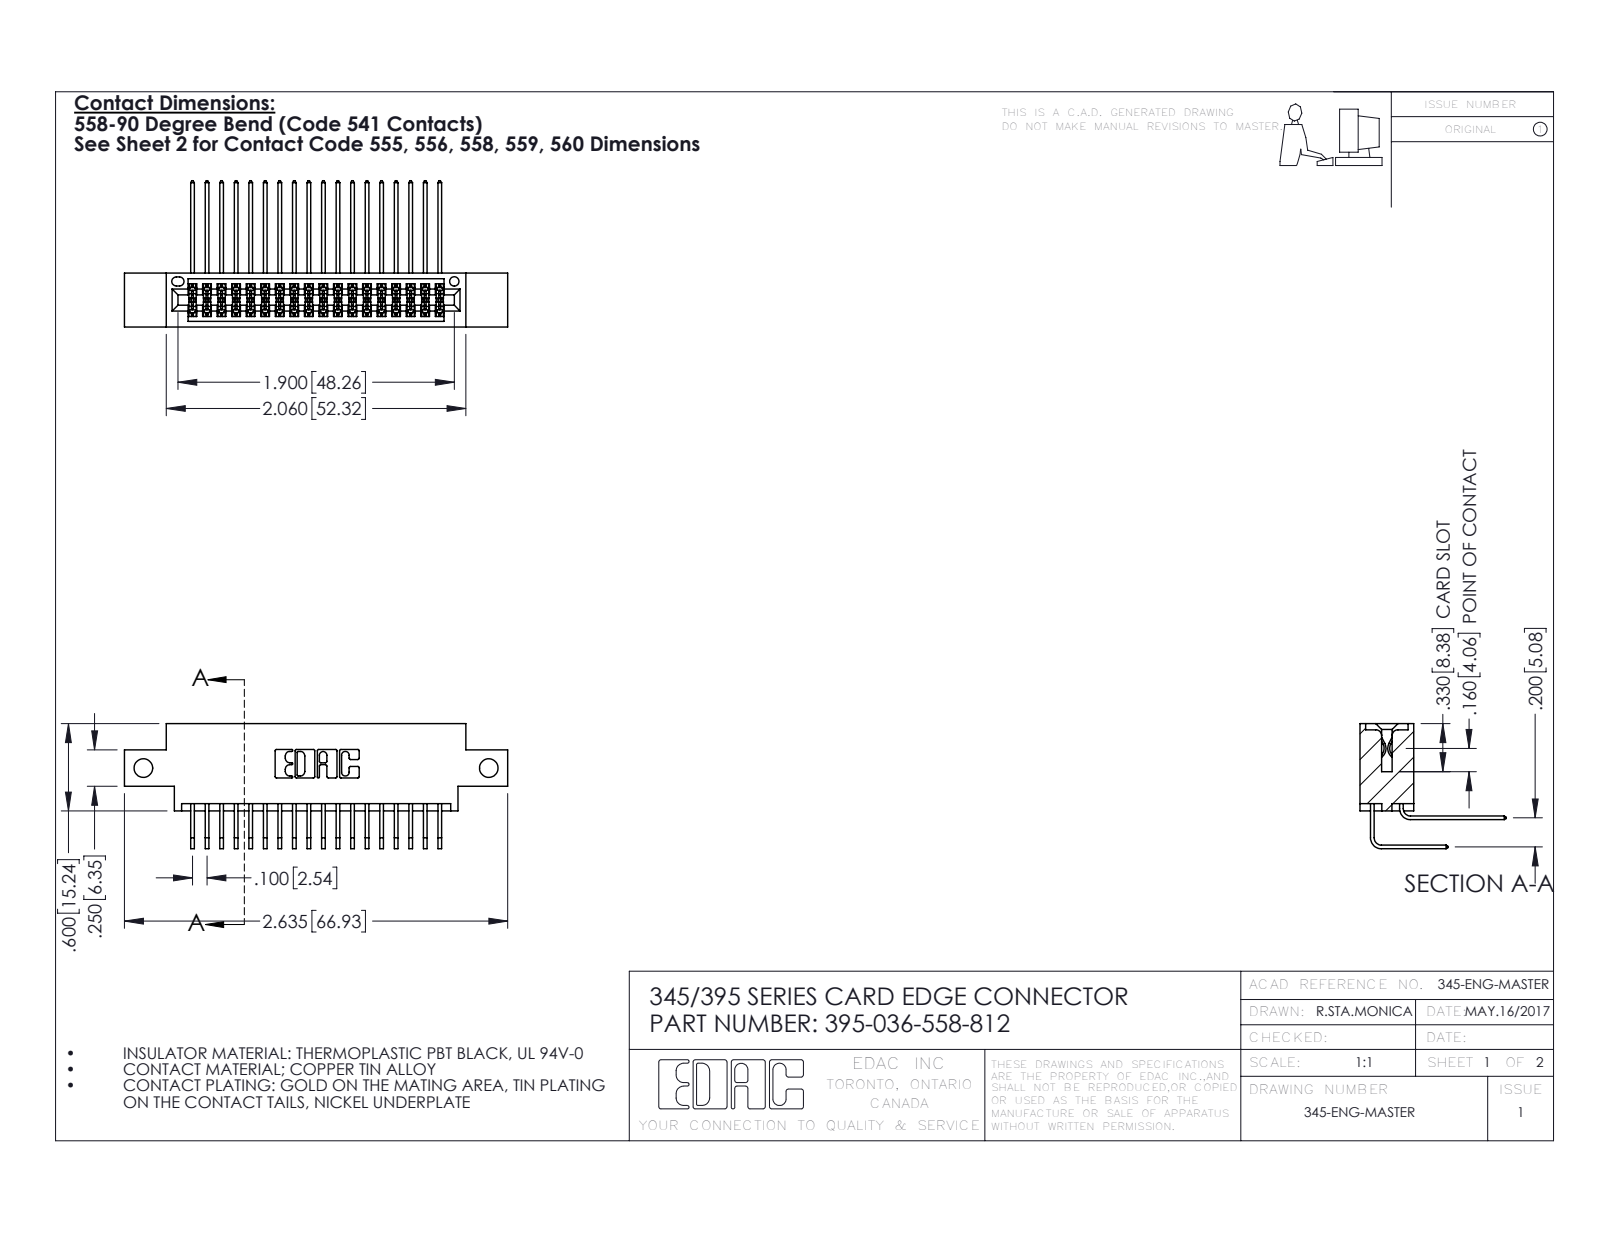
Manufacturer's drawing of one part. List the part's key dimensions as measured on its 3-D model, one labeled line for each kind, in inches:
Part name (STEP PRODUCT): 395-036-558-812; 345 Part_0.170 Offset - Side Mount; 345-292-001_558 Tail - 2; 345-292-001_558 559 Tail - 1
STEP written by: SolidWorks 2016 (CONFIG_CONTROL_DESIGN)
Units: inches
Bodies: 37 solids, 2002 faces (1344 planar, 658 cylindrical, 0 other)
Overall size (bounding box): 2.635 × 1.005 × 0.859
Volume: 0.384 in³ · Surface area: 15.21 in²
Round holes (diameter × count): ⌀0.128 ×2, ⌀0.064 ×1
Partial cylindrical surfaces — rounded edges, fillets, slot ends (radius × count): R0.006 ×55, R0.01 ×22, R0.007 ×6, R0.031 ×6, R0.026 ×3, R0.014 ×2, R0.019 ×2, R0.022 ×2
Main face-to-face distances: 0.2, 0.072, 0.298, 0.37, 0.098, 0.272, 0.025, 0.225, 0.175, 0.025
Hole centre spacings: 2.375
